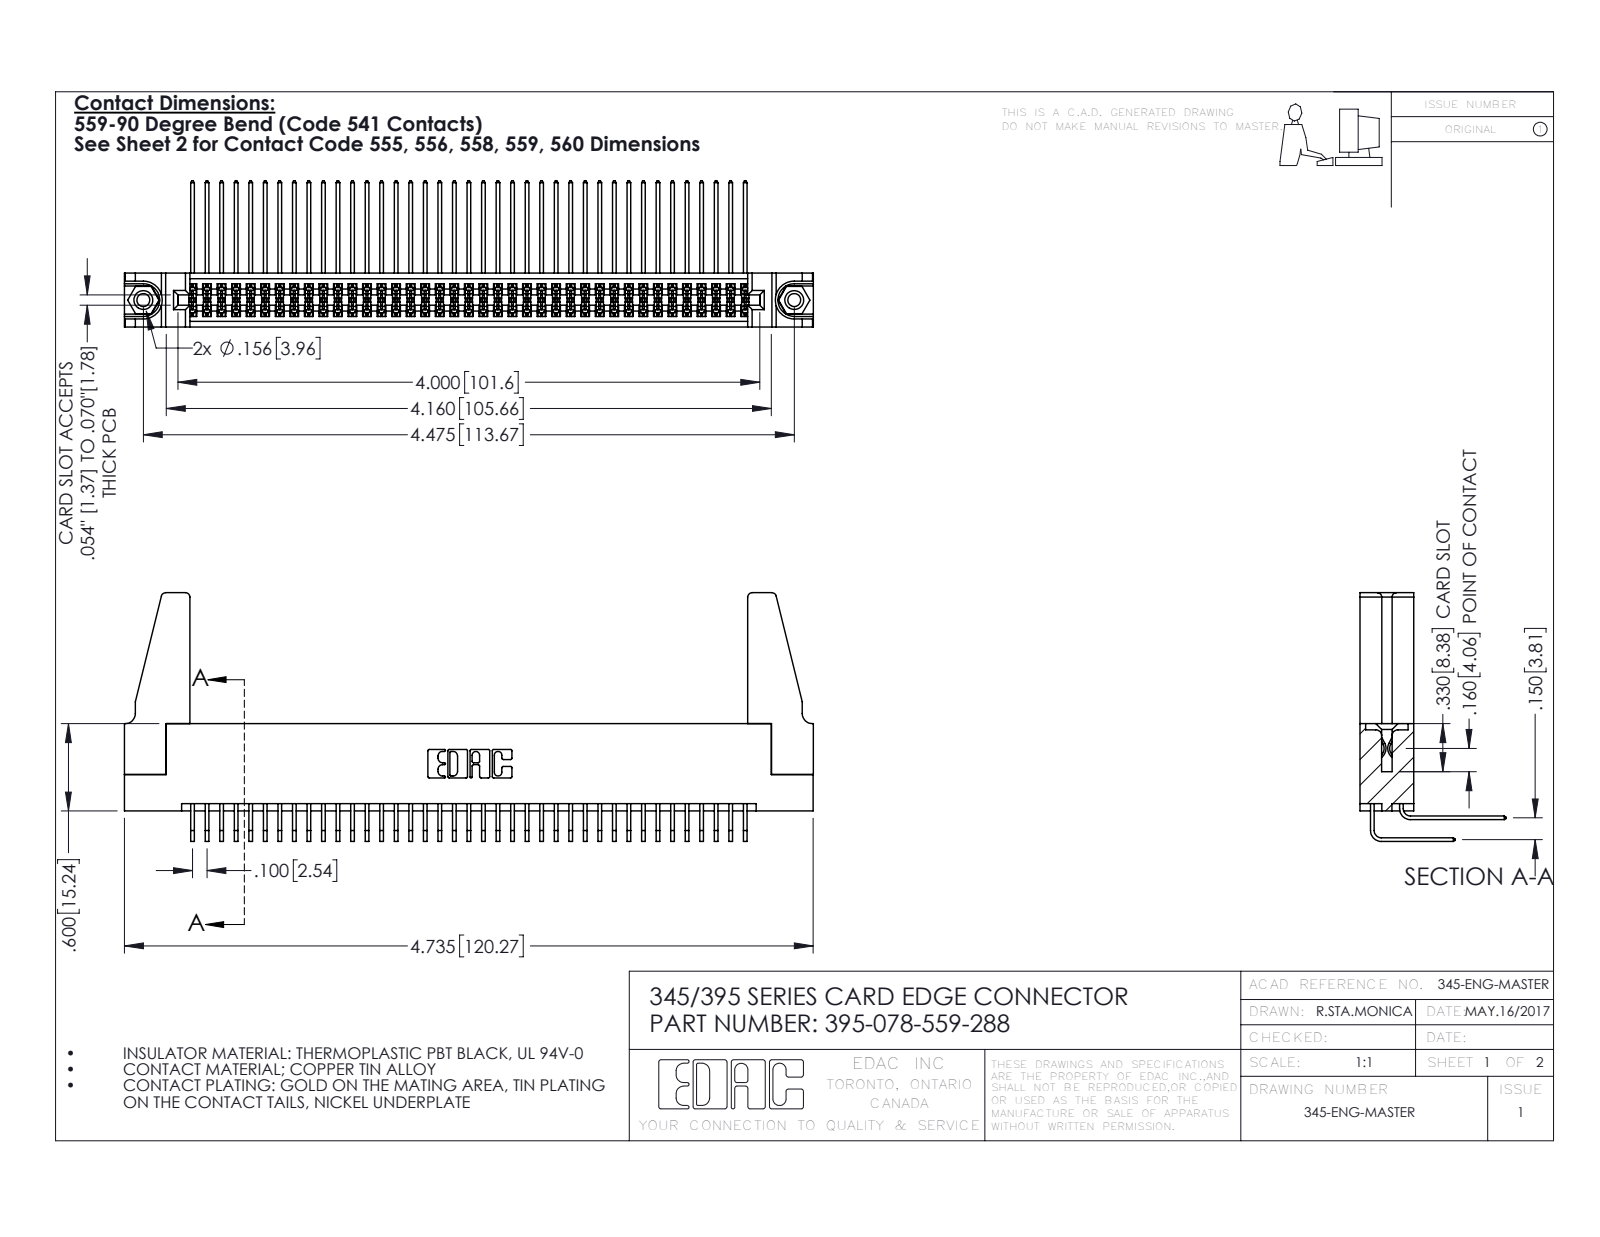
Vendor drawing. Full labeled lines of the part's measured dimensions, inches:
Part name (STEP PRODUCT): 395-078-559-288; 345-292-001_559 Tail - 2; 345-292-001_558 559 Tail - 1; 345-250-001_345-250-001-102 (+2 more)
STEP written by: SolidWorks 2016 (CONFIG_CONTROL_DESIGN)
Units: inches
Bodies: 83 solids, 4306 faces (2882 planar, 1408 cylindrical, 16 other)
Overall size (bounding box): 4.736 × 1.709 × 1.005
Volume: 0.937 in³ · Surface area: 35.77 in²
Round holes (diameter × count): ⌀0.089 ×2, ⌀0.125 ×2, ⌀0.156 ×2, ⌀0.064 ×1
Round bosses / shafts (diameter × count): ⌀0.155 ×2
Partial cylindrical surfaces — rounded edges, fillets, slot ends (radius × count): R0.006 ×117, R0.01 ×22, R0.03 ×8, R0.007 ×6, R0.031 ×6, R0.026 ×3, R0.014 ×2, R0.019 ×2
Main face-to-face distances: 0.072, 0.298, 0.37, 0.2, 0.098, 0.272, 0.025, 0.225, 0.175, 0.15
Hole centre spacings: 0.27, 4.239, 4.475
